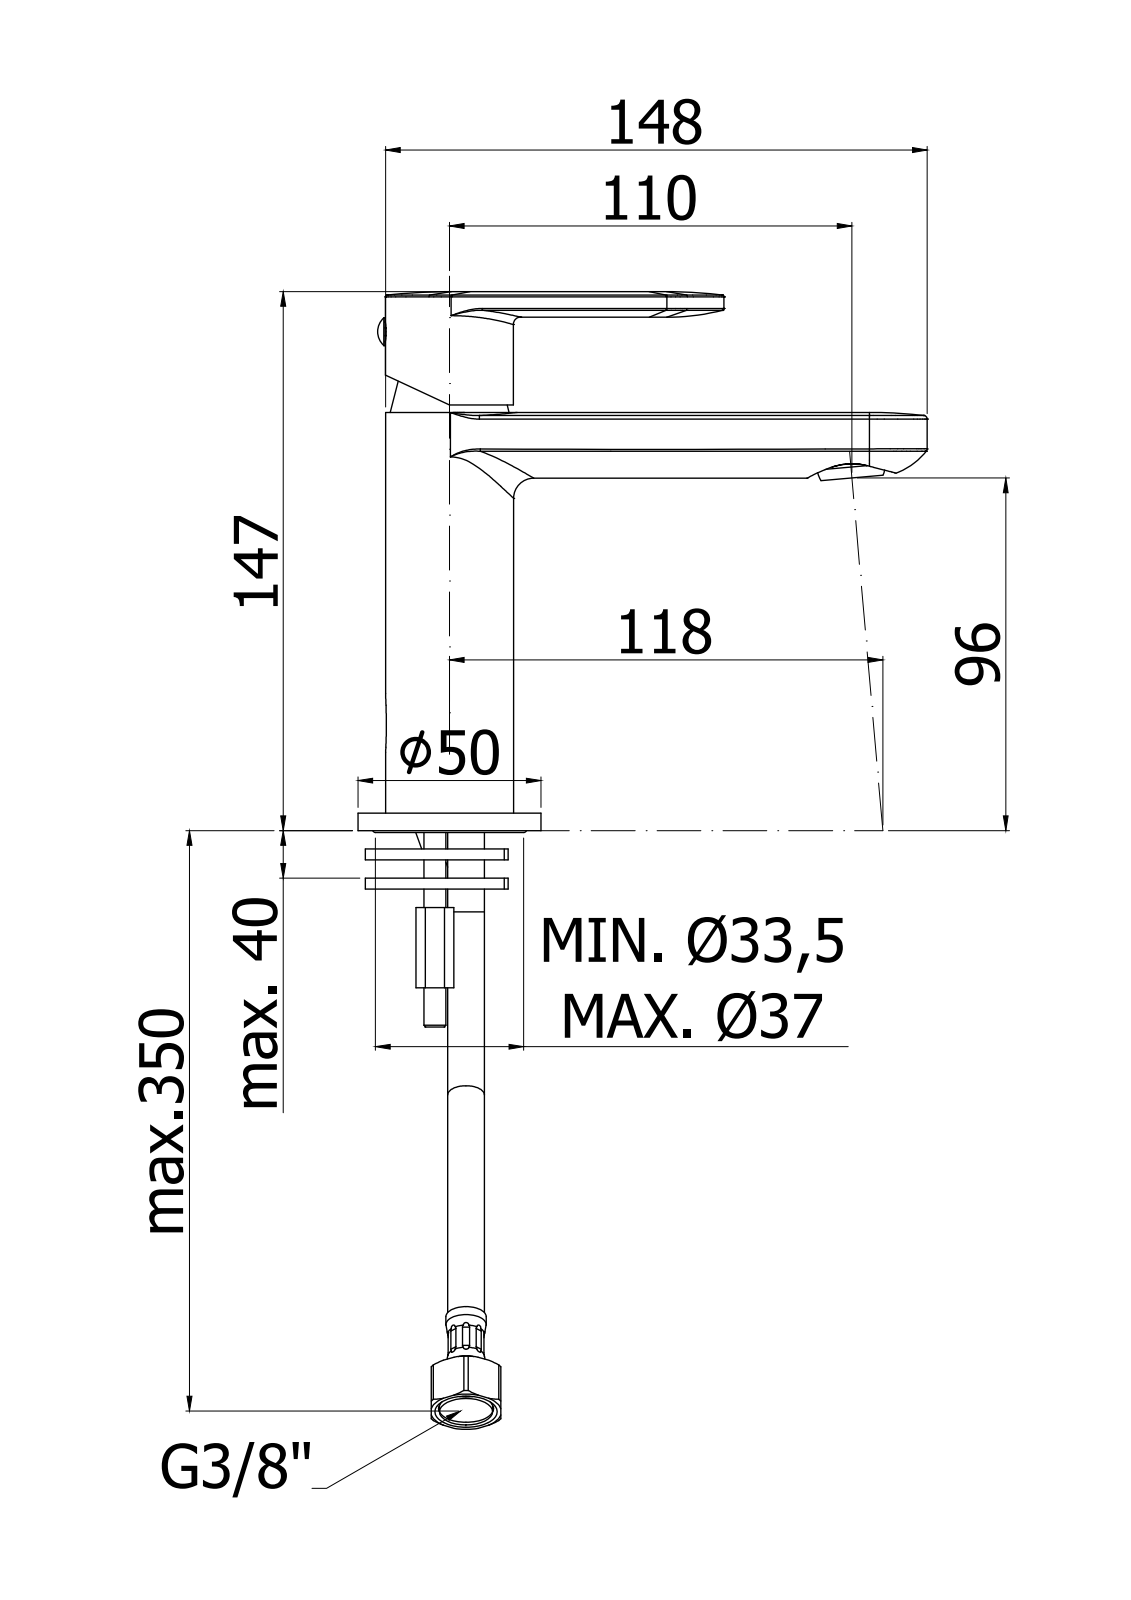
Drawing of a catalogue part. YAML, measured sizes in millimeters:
part_name: "CA071CR_SW0001"
step_written_by: "CREO PARAMETRIC BY PTC INC, 2020044 (CONFIG_CONTROL_DESIGN)"
units: millimeters
bodies: {solids: 2, faces: 471, planar: 104, cylindrical: 145, other: 222}
overall_size: [155.5, 145.92, 50]
volume: 98667
surface_area: 64778
round_holes:
  - {diameter: 3.2, count: 2}
  - {diameter: 5, count: 2}
  - {diameter: 5.5, count: 2}
  - {diameter: 7, count: 2}
  - {diameter: 8.6, count: 2}
  - {diameter: 9.4, count: 2}
  - {diameter: 3, count: 1}
  - {diameter: 4.2, count: 1}
  - {diameter: 4.5, count: 1}
  - {diameter: 16, count: 1}
  - {diameter: 17.5, count: 1}
  - {diameter: 24.5, count: 1}
round_bosses_or_shafts:
  - {diameter: 35, count: 2}
  - {diameter: 50, count: 1}
  - {diameter: 31.8, count: 1}
  - {diameter: 27.4, count: 1}
  - {diameter: 24.5, count: 1}
  - {diameter: 24, count: 1}
  - {diameter: 18.5, count: 1}
  - {diameter: 7.6, count: 1}
partial_cylinders:
  - {radius: 1, count: 11}
  - {radius: 0.5, count: 8}
  - {radius: 1.5, count: 4}
  - {radius: 3, count: 4}
  - {radius: 5, count: 2}
  - {radius: 16, count: 2}
  - {radius: 3.5, count: 1}
  - {radius: 9.75, count: 1}
face_to_face_distances: [4, 3, 0.69, 3.31, 142.92, 142.23, 138.92, 85.9, 85.21, 81.9]
hole_center_spacings: [11, 1.52, 3, 6.72, 7.7, 8.68, 8.94, 9.33]
